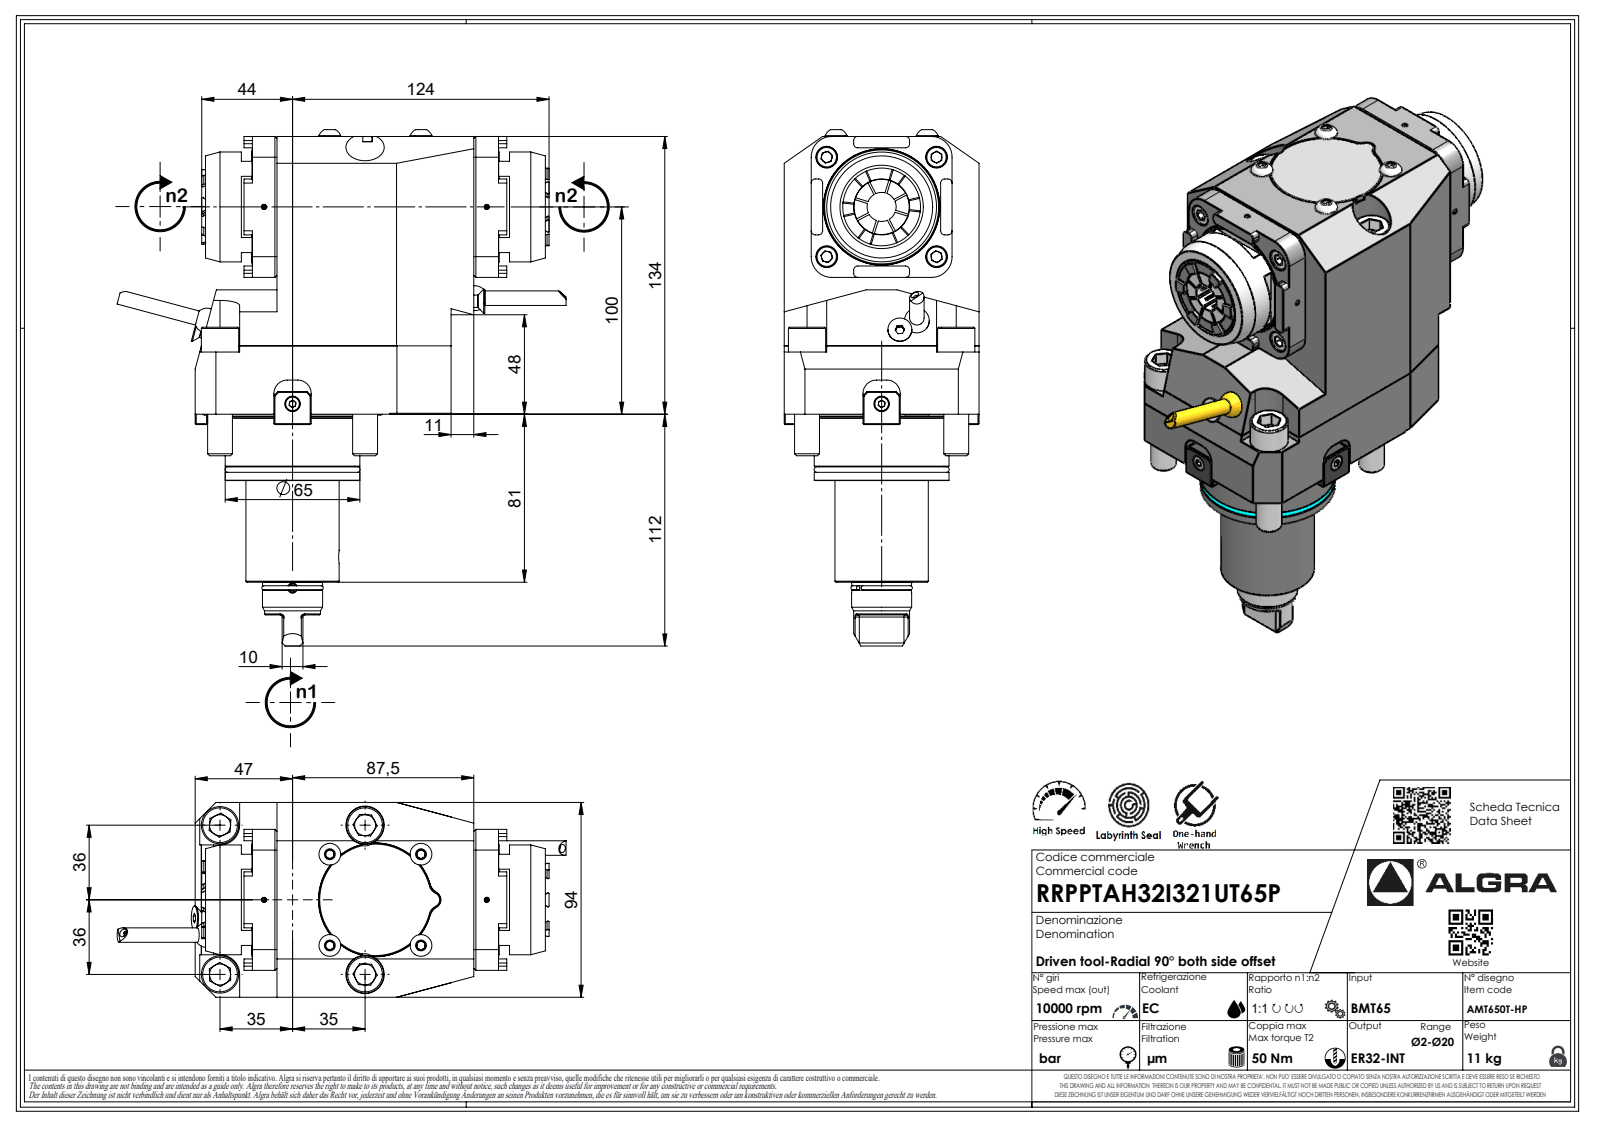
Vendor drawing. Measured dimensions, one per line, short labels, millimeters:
name: RRPPTAH32I321UT65P
written by: SolidWorks 2023 (AUTOMOTIVE_DESIGN)
unit: mm
bodies: 1 solid, 653 faces (426 planar, 101 cylindrical, 126 other)
size: 249.1 × 216.66 × 94
volume: 1 686 000 mm³; area: 113 052 mm²
holes: 1× ⌀2.1
bosses: 4× ⌀12, 4× ⌀10.5, 2× ⌀18, 2× ⌀7, 1× ⌀65, 1× ⌀64.6, 1× ⌀60.2, 1× ⌀53
rounds: 16× R2, 7× R0.33, 7× R0.52, 7× R3.7, 6× R1, 4× R10, 2× R9.5, 1× R0.21
face distances: 94, 134, 34.5, 129.5, 81, 22.6, 141.4, 11.9, 106.9, 68
